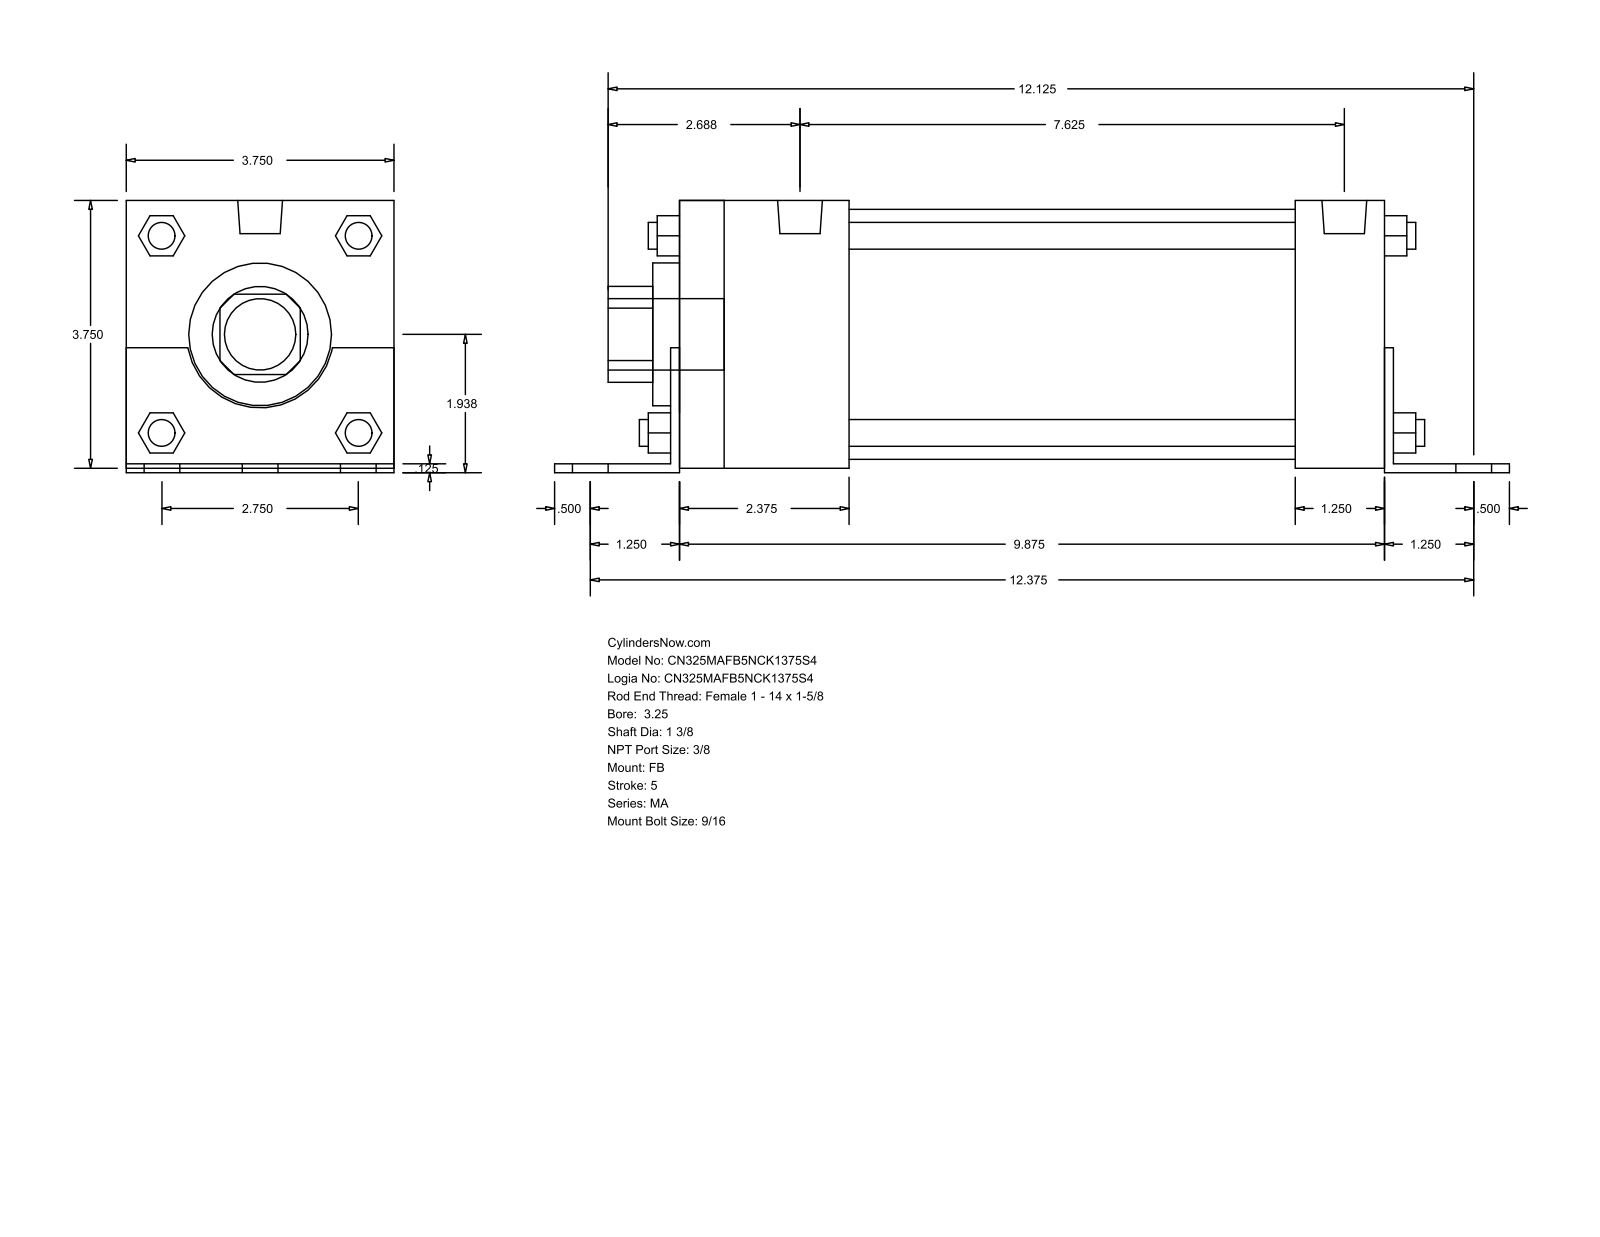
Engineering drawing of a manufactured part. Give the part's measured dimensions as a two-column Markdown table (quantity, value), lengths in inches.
| quantity | value |
| --- | --- |
| part name | MA_FB__0325_1.375 |
| STEP written by | GSSL Pune (CONFIG_CONTROL_DESIGN) |
| units | inches |
| bodies | 0 solids, 140 faces (105 planar, 35 cylindrical, 0 other) |
| overall size | 13.375 × 3.813 × 3.75 |
| round holes (diameter × count) | 1.375 × 1, 2 × 1, 3.5 × 1 |
| round bosses / shafts (diameter × count) | 0.563 × 6, 0.437 × 4, 0.375 × 4, 0.627 × 2, 1 × 1 |
| partial cylindrical surfaces (radius × count) | 0.672 × 1, 1.03 × 1 |
| main face-to-face distances | 3.75, 0.125, 0.063, 3.812, 0.062, 3.687, 10, 9.875, 1.375, 2.375 |
